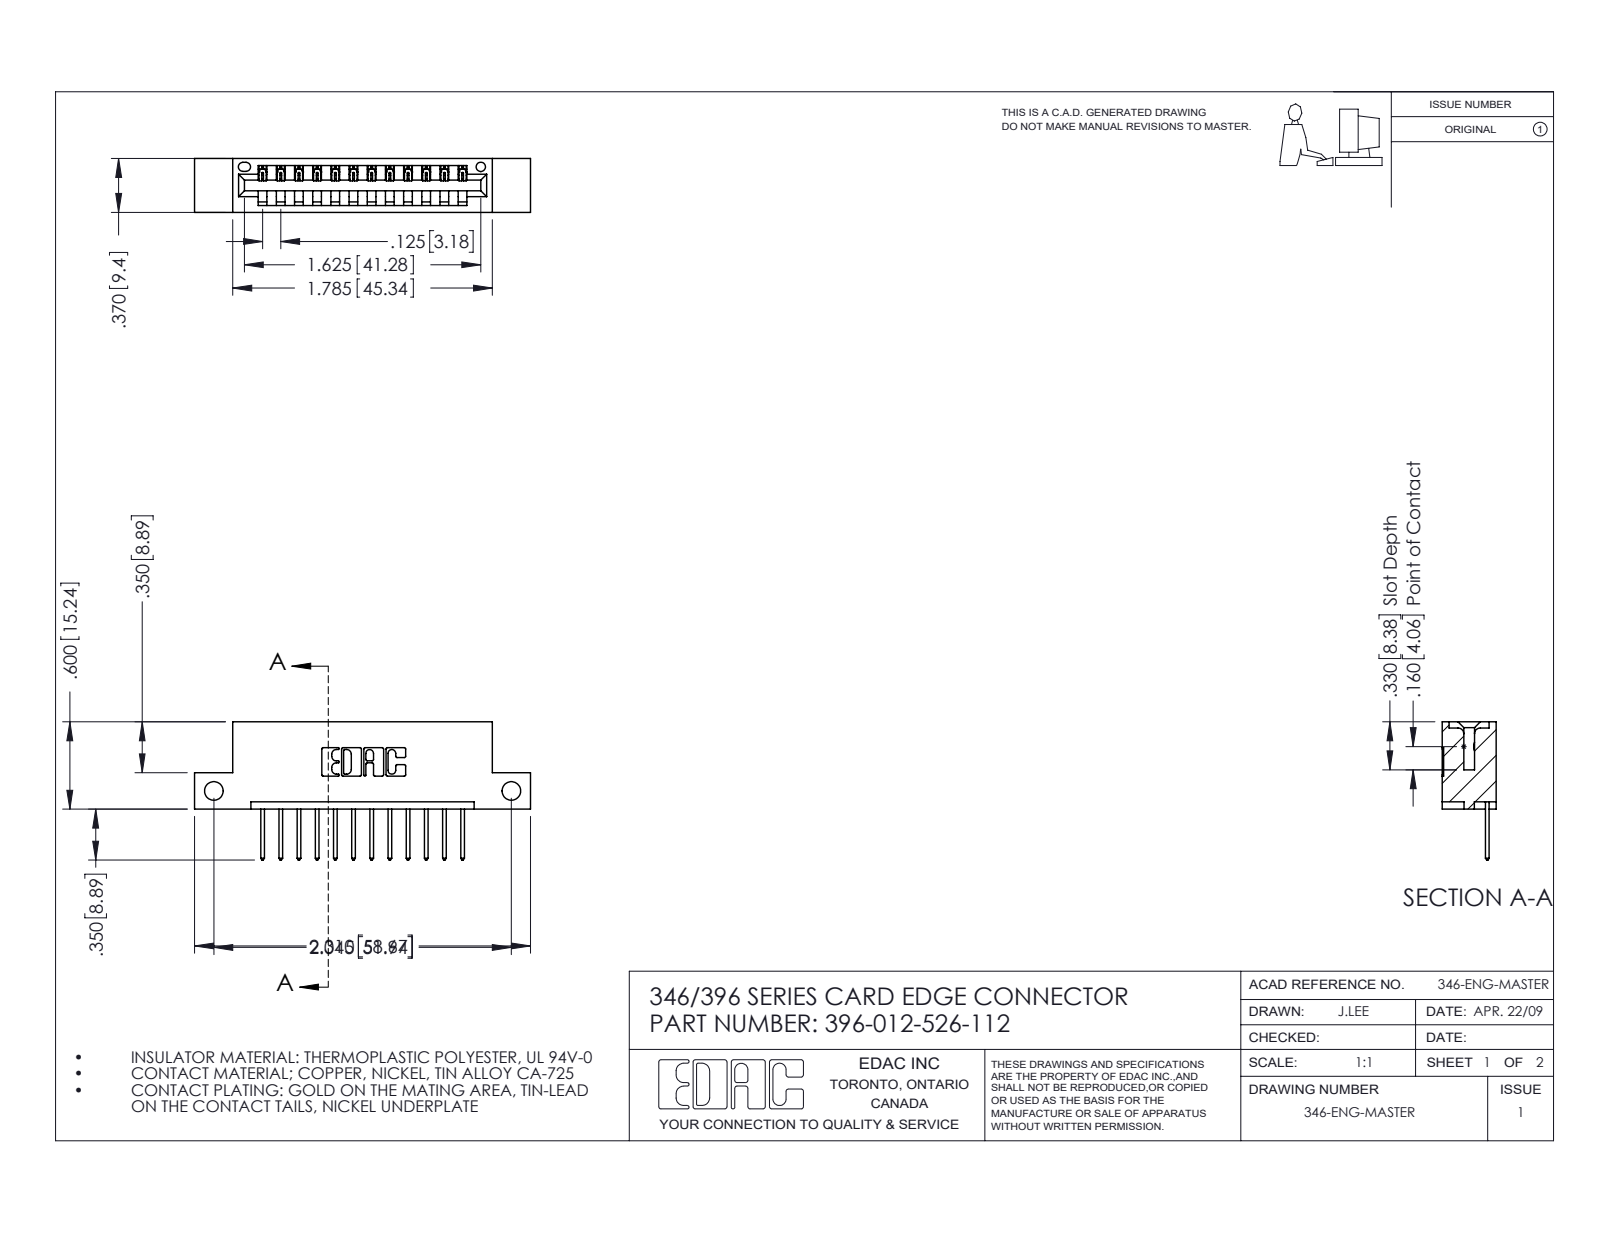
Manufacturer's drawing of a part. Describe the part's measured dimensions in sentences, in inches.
The part is named "396-012-526-112; 345-292-001_345-293-126; 346 Part_Flush Mounting Lugs - Side Mount". Its 3-D file was written by "SolidWorks 2016 (CONFIG_CONTROL_DESIGN)". It is 13 solids with 818 faces: 556 planar, 262 cylindrical and 0 other. Overall it measures 2.31 by 0.95 by 0.37 inches. Its volume is 0.324 cubic inches and its surface area 9.547 square inches. Round holes: 2 of diameter 0.128, 1 of diameter 0.064. Partial cylindrical surfaces (rounded edges, fillets, slot ends): 24 of radius 0.006, 24 of radius 0.01, 22 of radius 0.01, 6 of radius 0.007, 6 of radius 0.031, 3 of radius 0.026, 2 of radius 0.031, 2 of radius 0.04. The main face-to-face distances are 0.25, 0.048, 0.322, 0.37, 0.072, 0.298, 0.025, 0.148, 0.222, 0.1. The hole center spacings are 2.045.
